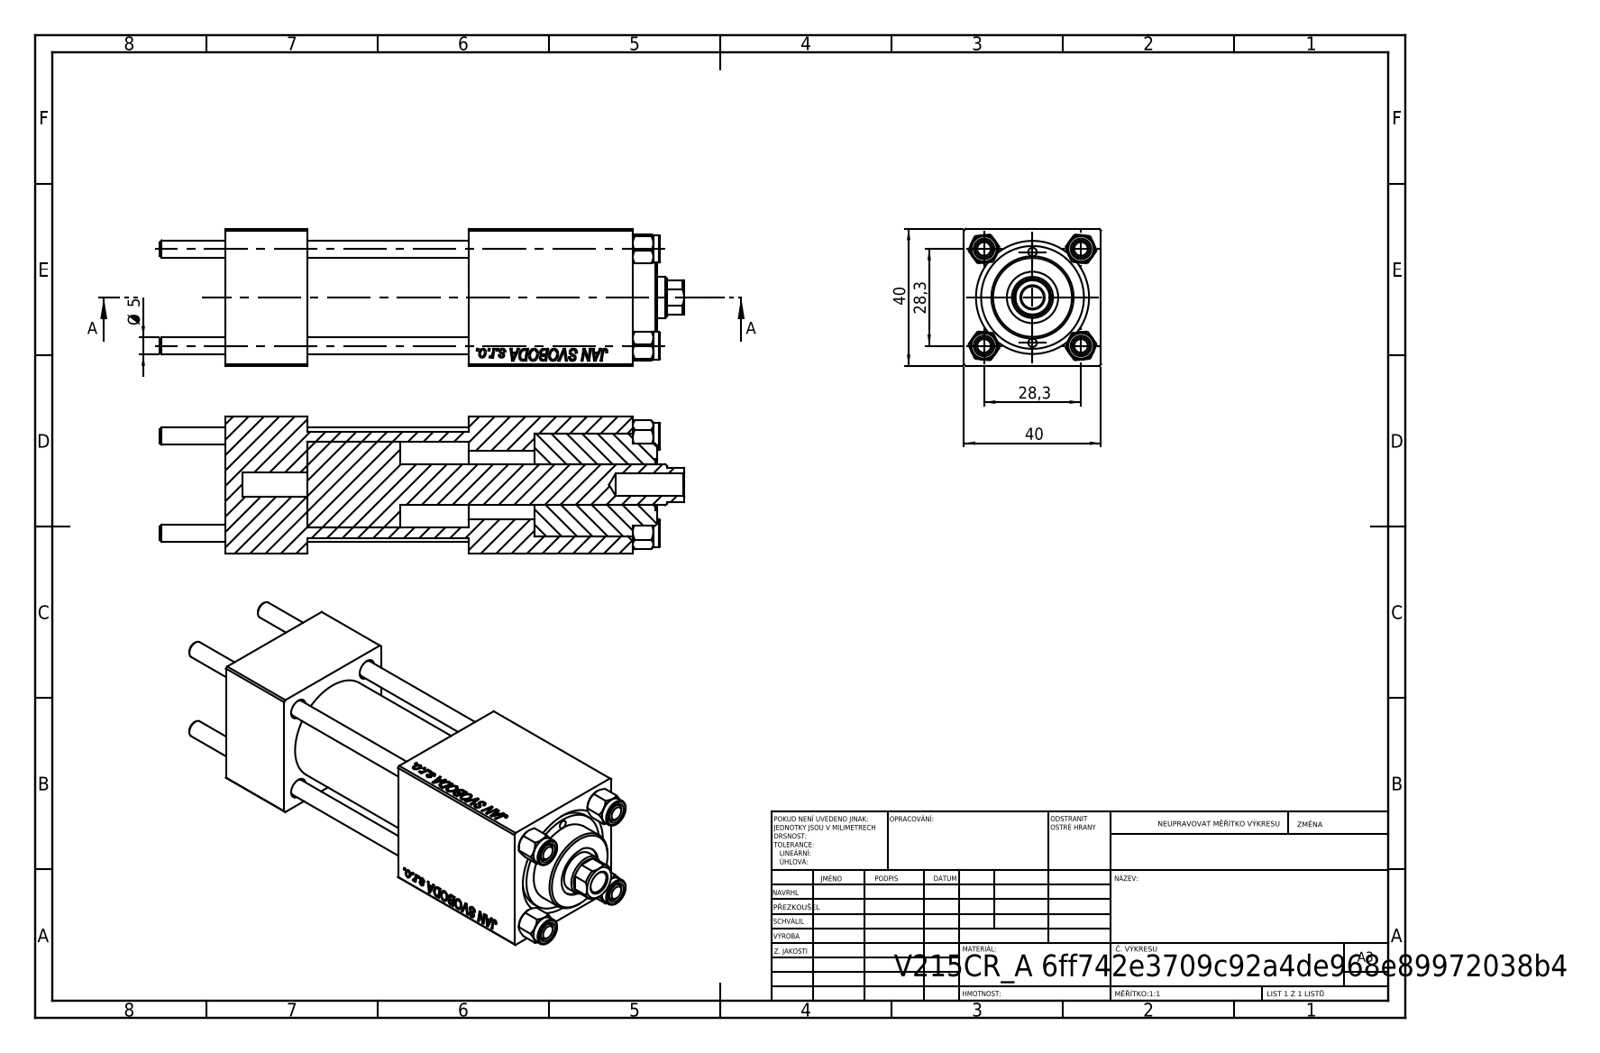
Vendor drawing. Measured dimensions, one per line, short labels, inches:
name: CR025_012_A_0_G_A_G_M_020_+#_##_TYCINKA; V215CR_VCP; V215CR_BODY_A; V215_VC_A (+1 more)
written by: SolidWorks 2019 (CONFIG_CONTROL_DESIGN)
unit: in
bodies: 11 solids, 1137 faces (519 planar, 82 cylindrical, 536 other)
size: 6.024 × 1.575 × 1.575
volume: 8.835 in³; area: 91.37 in²
holes: 4× ⌀0.197, 3× ⌀0.787, 2× ⌀0.098, 2× ⌀0.276, 2× ⌀0.518, 1× ⌀0.256, 1× ⌀0.472, 1× ⌀0.591, 1× ⌀0.984, 1× ⌀1.181
bosses: 4× ⌀0.315, 1× ⌀1.22, 1× ⌀0.945
rounds: 1× R0.217
face distances: 1.575, 0.945, 3.555, 2.61, 4.685, 3.74, 1.13, 2.795, 1.85, 0.76
hole spacings: 0.558, 0.788, 1.114, 1.214, 0.522, 1.576, 1.043, 2.835
